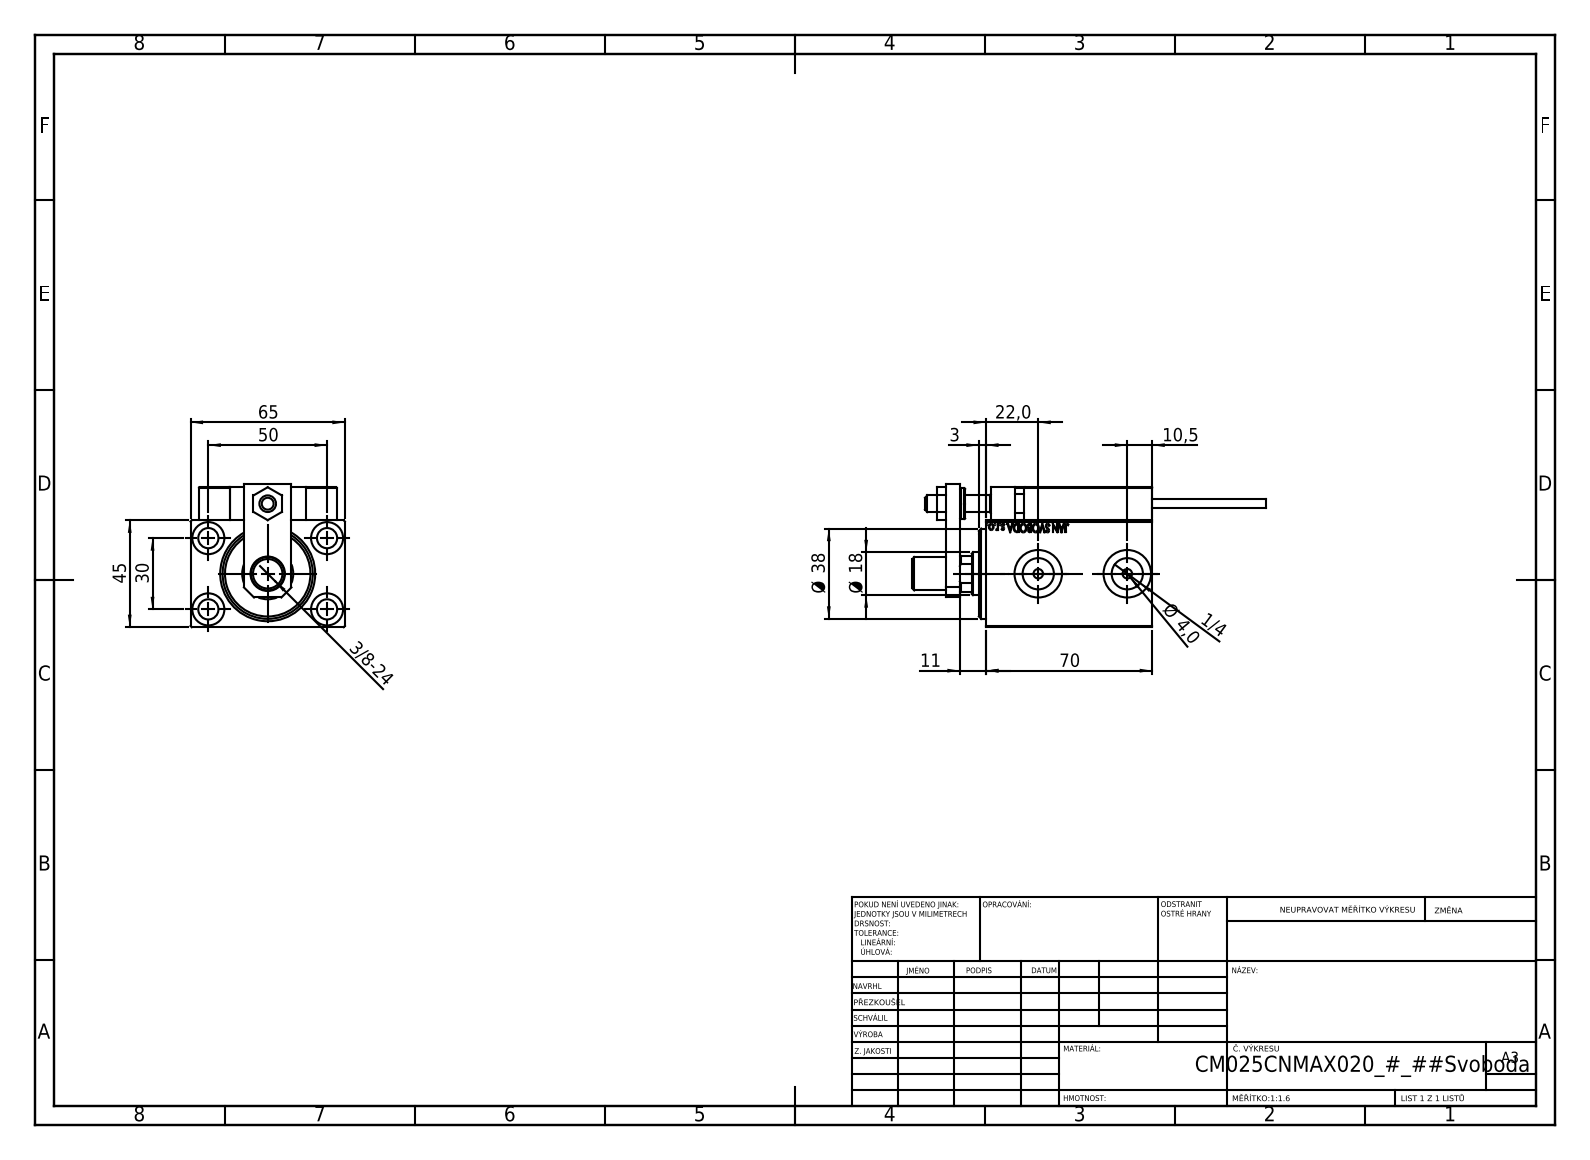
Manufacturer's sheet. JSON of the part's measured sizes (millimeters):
{"part_name": "KONCOVKA; Block; MAGNET; V450CM_C_Body (+7 more)", "step_written_by": "SolidWorks 2019 (CONFIG_CONTROL_DESIGN)", "units": "millimeters", "bodies": {"solids": 24, "faces": 1295, "planar": 563, "cylindrical": 192, "other": 540}, "overall_size": [149, 65, 60.5], "volume_mm3": 226016, "surface_area_mm2": 70376, "round_holes": [[4, 6], [8, 5], [8.5, 5], [3.2, 4], [13.5, 4], [5, 2], [13.16, 2], [20, 2], [7, 1], [14.5, 1], [18, 1], [21.5, 1]], "round_bosses_or_shafts": [[5, 2], [3.8, 2], [14, 1], [13, 1], [12, 1], [11, 1]], "partial_cylinders_radius": [[0.3, 30], [3, 2], [8.5, 1]], "face_to_face_distances": [45, 59, 14, 65, 6, 3, 19, 5, 7, 20], "hole_center_spacings": [29.15, 11.37, 20, 22.09, 28.9, 29.59, 29.69, 30]}
